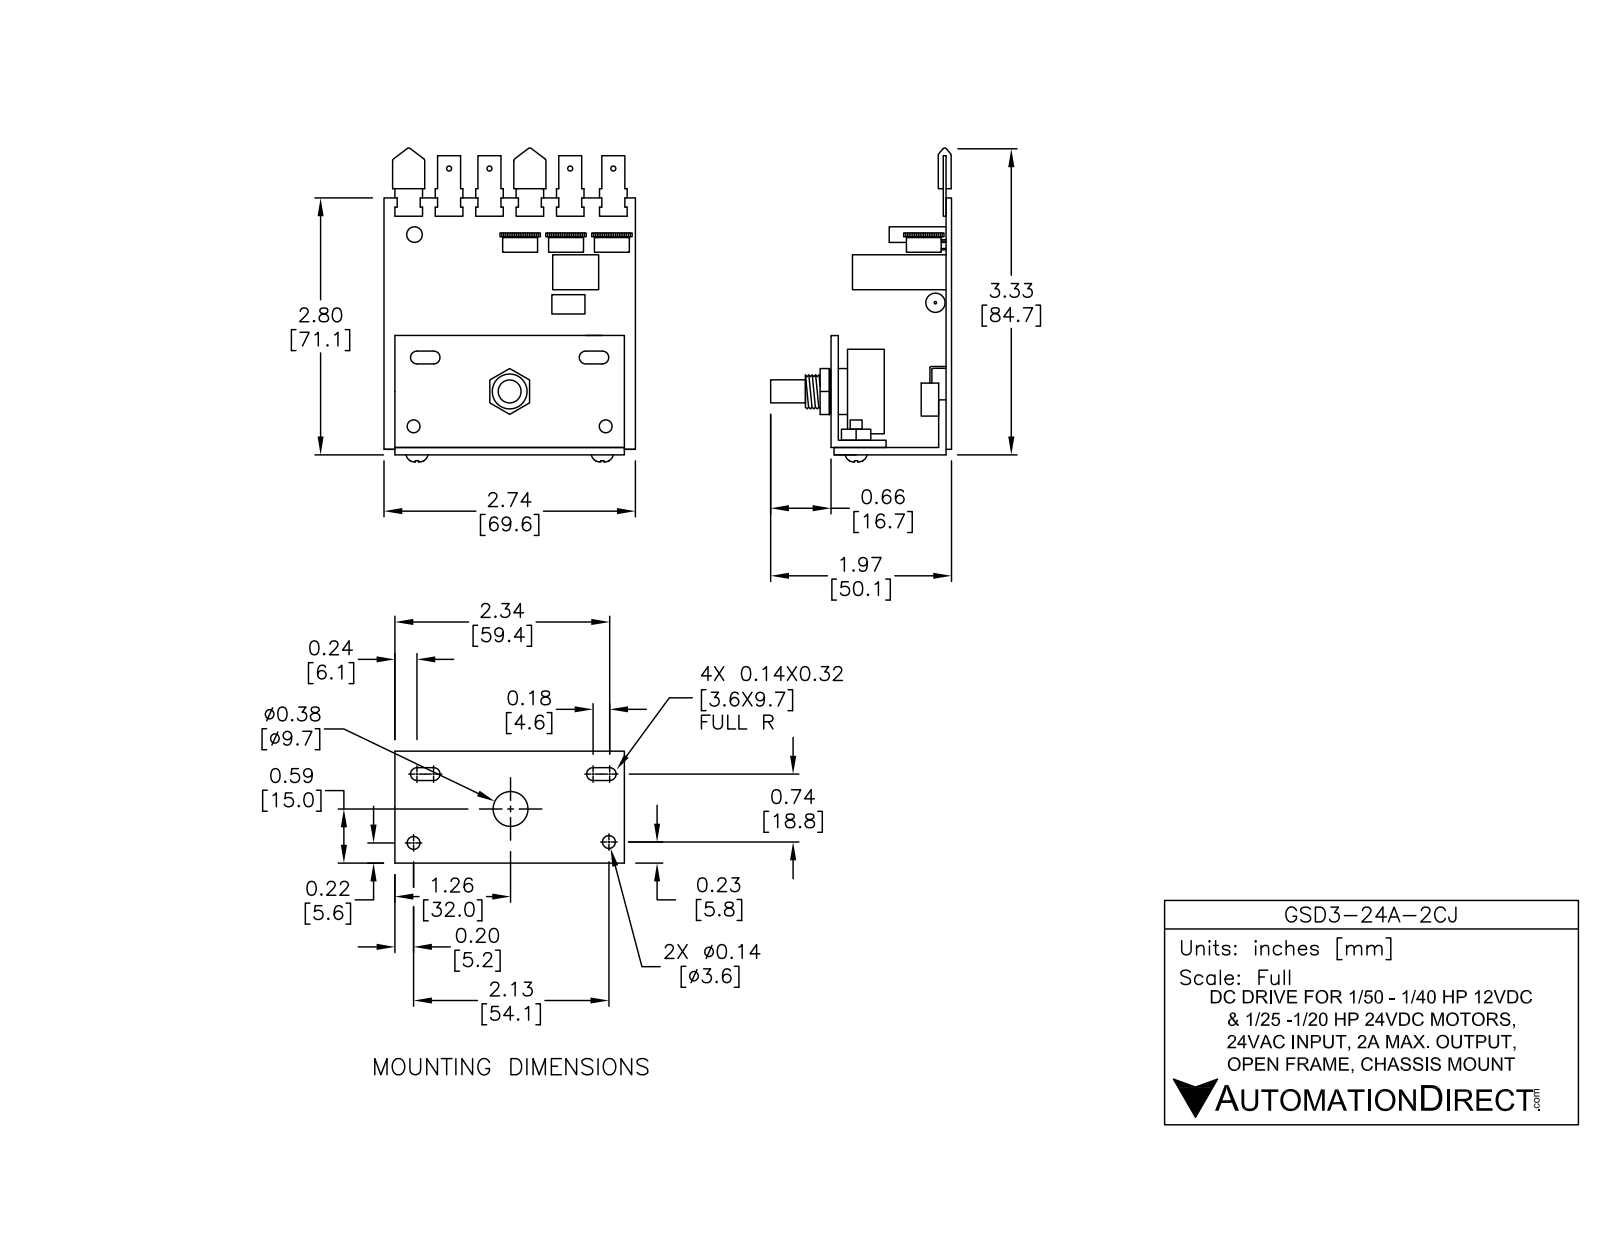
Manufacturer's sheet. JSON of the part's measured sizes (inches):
{"part_name": "Q5; SOT23; TO-220AB-FLAT-_150P-P; GSD3-24A-2CJ (+7 more)", "step_written_by": "SolidWorks 2014 (AUTOMOTIVE_DESIGN)", "units": "inches", "bodies": {"solids": 112, "faces": 3389, "planar": 2133, "cylindrical": 1060, "other": 196}, "overall_size": [3.303, 2.734, 2.016], "volume_in3": 2.16, "surface_area_in2": 59.35, "round_holes": [[0.026, 22], [0.052, 18], [0.033, 15], [0.043, 14], [0.046, 14], [0.14, 14], [0.067, 11], [0.04, 6], [0.08, 4], [0.11, 4], [0.144, 4], [0.048, 3]], "round_bosses_or_shafts": [[0.022, 8], [0.026, 6], [0.025, 6], [0.25, 5], [0.156, 4], [0.354, 3], [0.106, 3], [0.051, 3]], "partial_cylinders_radius": [[0.004, 48], [0.025, 23], [0.05, 12], [0.02, 8], [0.07, 8], [0.039, 4], [0.091, 4], [0.225, 3]], "face_to_face_distances": [0.08, 0.063, 1.15, 1.23, 1.293, 1.213, 1.07, 0.143, 0.16, 1.195], "hole_center_spacings": [0.15, 0.3, 0.451, 0.58, 0.801, 0.151, 0.225, 0.233]}
